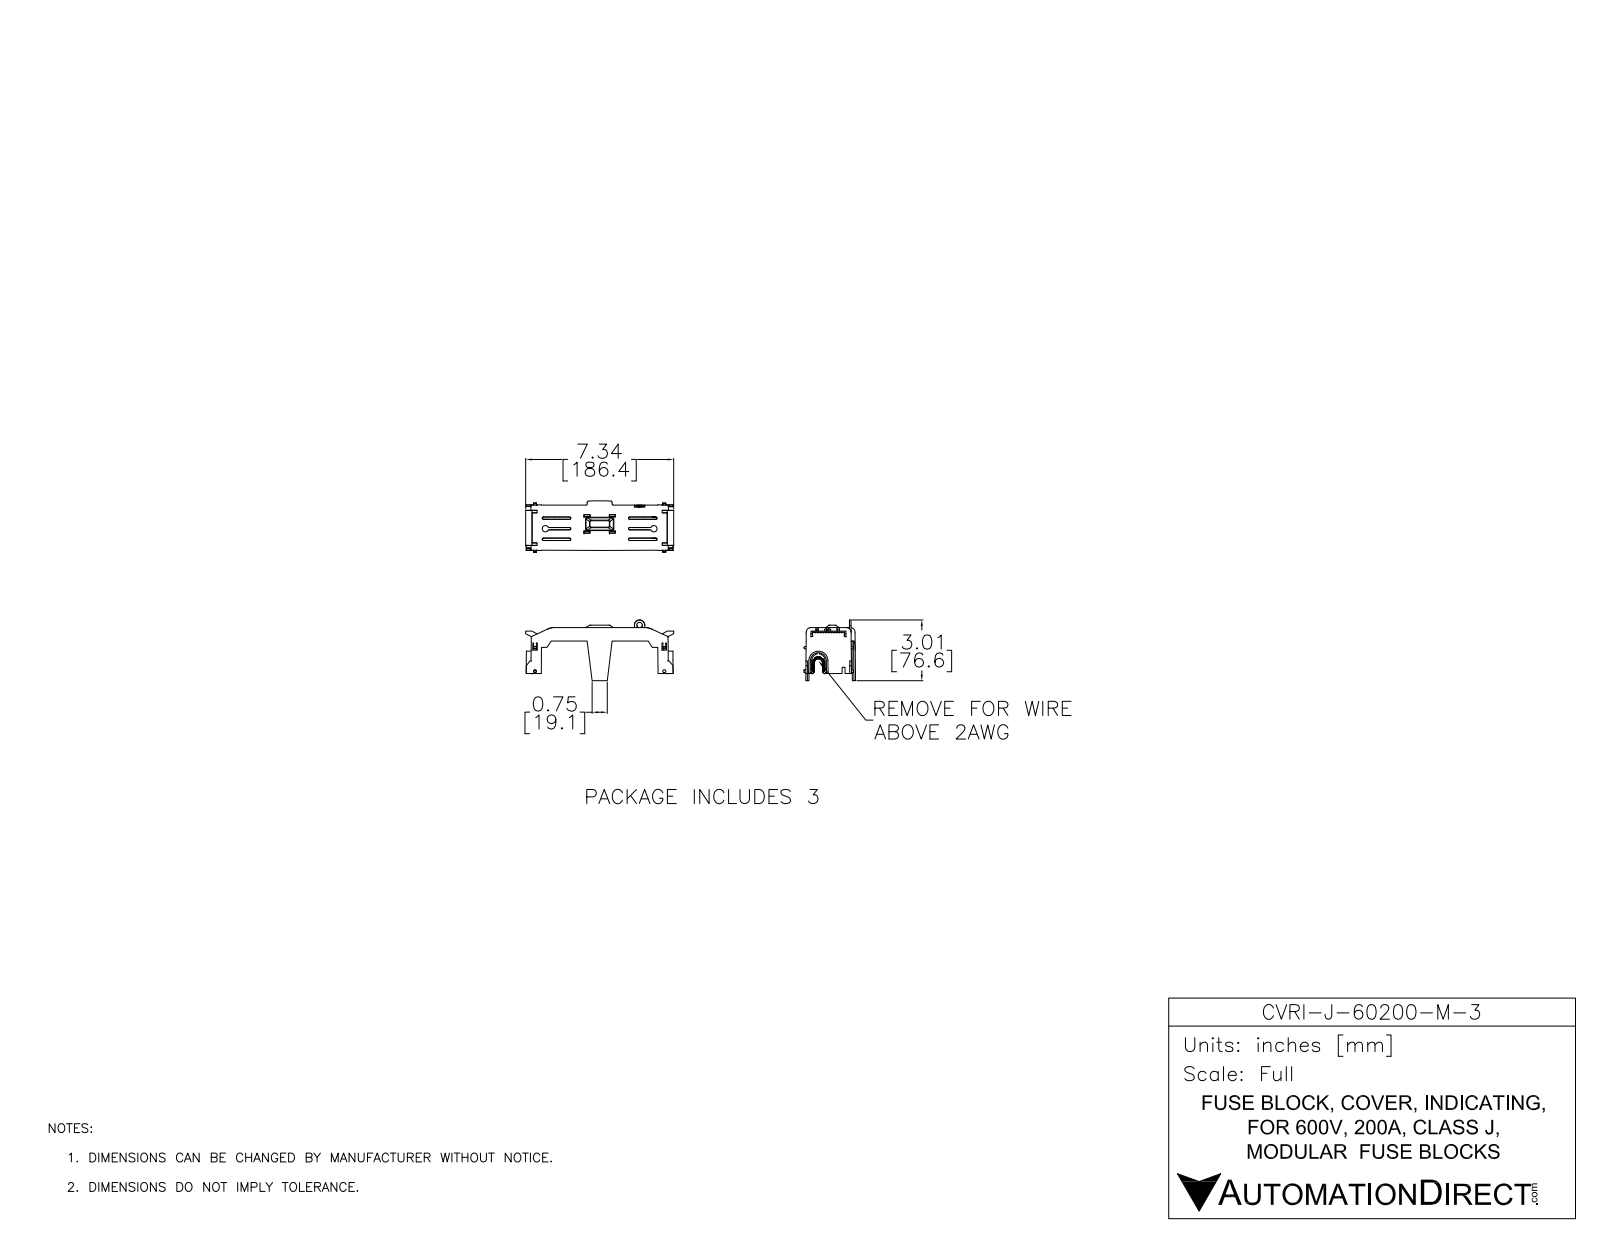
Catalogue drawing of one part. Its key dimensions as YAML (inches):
part_name: "CVRI-J-60200-M-3"
step_written_by: "SolidWorks 2017 (AUTOMOTIVE_DESIGN)"
units: inches
bodies: {solids: 1, faces: 1408, planar: 920, cylindrical: 113, other: 375}
overall_size: [7.34, 3.014, 2.553]
volume: 3.494
surface_area: 95.88
round_holes:
  - {diameter: 0.276, count: 1}
partial_cylinders:
  - {radius: 0.039, count: 12}
  - {radius: 0.236, count: 9}
  - {radius: 0.118, count: 8}
  - {radius: 0.157, count: 7}
  - {radius: 0.035, count: 6}
  - {radius: 0.059, count: 4}
  - {radius: 0.01, count: 2}
  - {radius: 0.02, count: 2}
face_to_face_distances: [0.079, 0.197, 0.118, 0.276, 0.512, 0.606, 0.095, 0.174, 0.803, 0.256]
